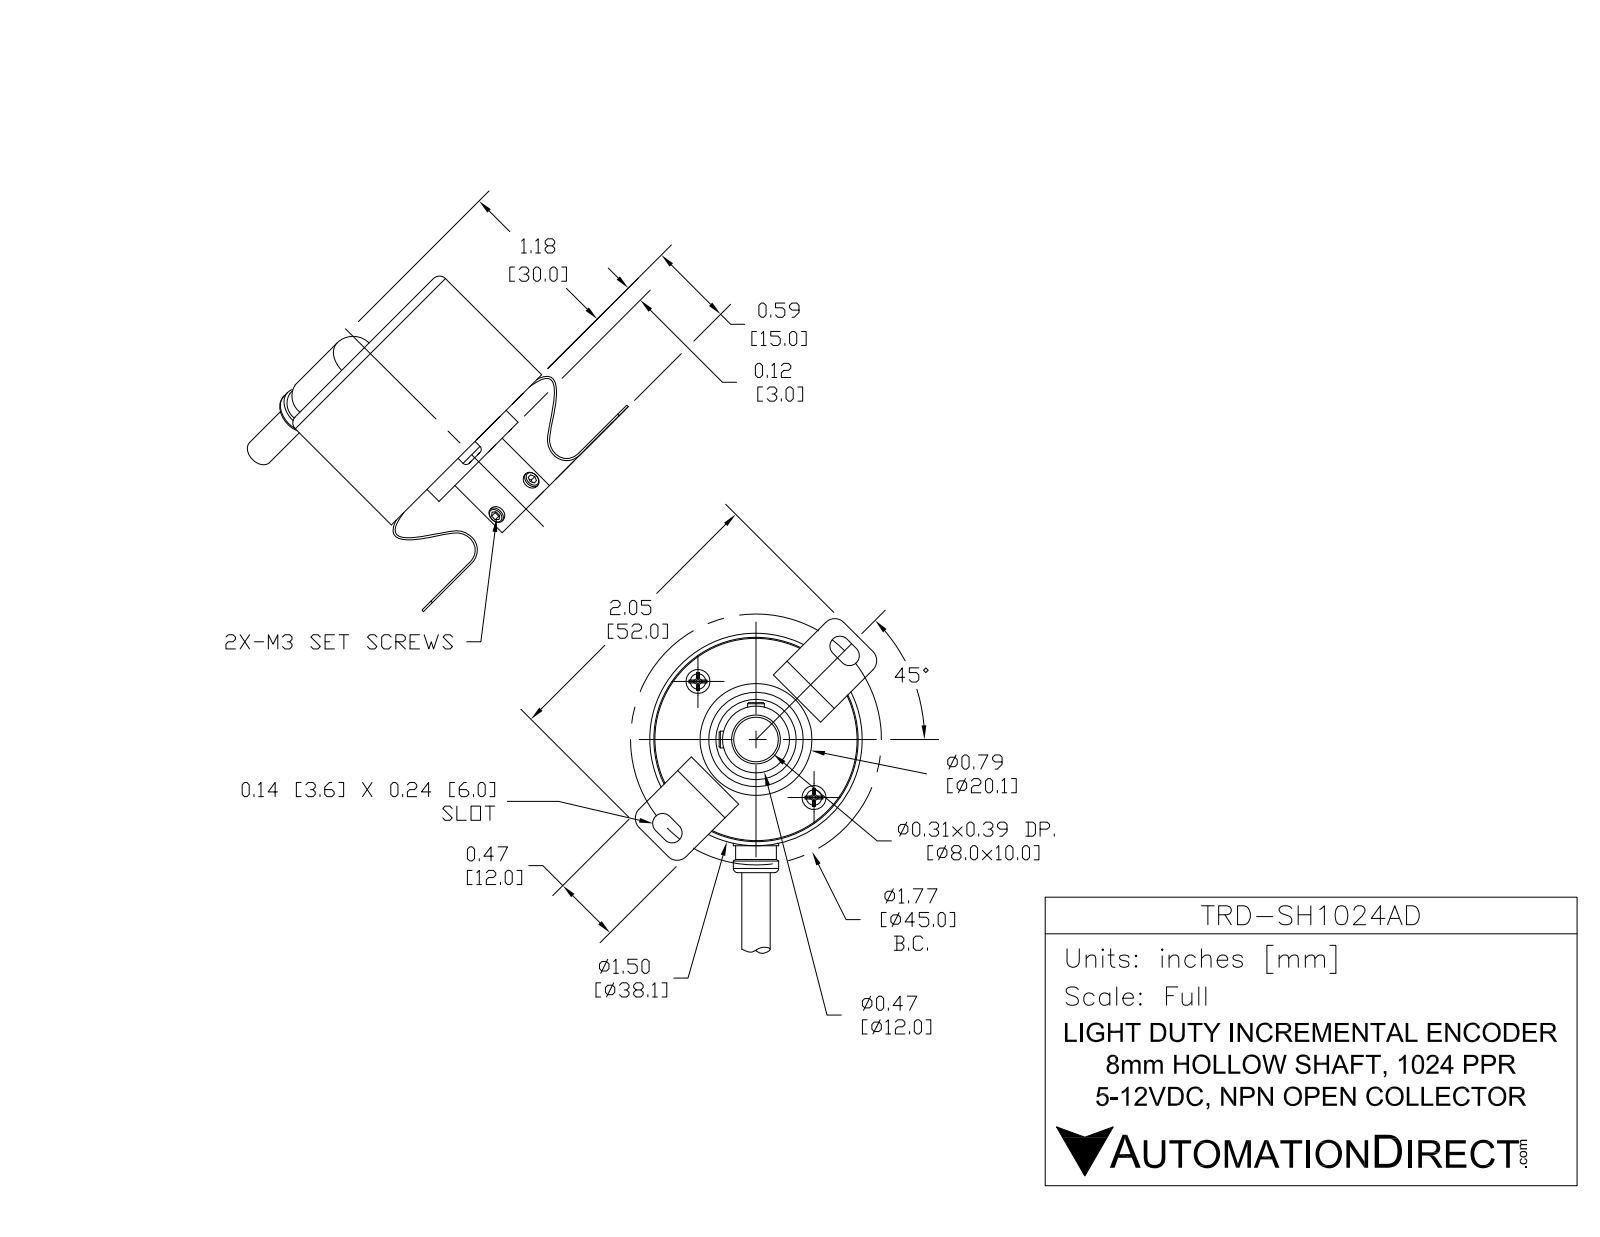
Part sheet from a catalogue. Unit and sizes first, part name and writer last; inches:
Units: inches
Overall size (bounding box): 3.952 × 1.772 × 1.684
Round holes (diameter × count): ⌀0.126 ×5, ⌀0.098 ×2, ⌀0.315 ×1, ⌀0.791 ×1
Round bosses / shafts (diameter × count): ⌀0.118 ×5, ⌀1.496 ×1, ⌀0.787 ×1, ⌀0.591 ×1, ⌀0.472 ×1, ⌀0.299 ×1, ⌀0.197 ×1, ⌀0.134 ×1
Partial cylindrical surfaces — rounded edges, fillets, slot ends (radius × count): R0.039 ×6, R0.118 ×5, R0.03 ×4, R0.071 ×4, R0.087 ×4, R0.098 ×4, R0.031 ×2, R0.146 ×2
Main face-to-face distances: 1.024, 0.579, 1.035, 0.591, 1.614, 1.602, 0.567, 0.118, 1.142, 0.106
Hole centre spacings: 0.551, 0.78, 0.955, 0.285, 0.285, 0.954, 1.065, 1.065
Volume: 2.043 in³ · Surface area: 17.32 in²
Bodies: 11 solids, 322 faces (169 planar, 101 cylindrical, 52 other)
Part name (STEP PRODUCT): TRD-SH1024AD
STEP written by: SolidWorks 2016 (AUTOMOTIVE_DESIGN)
